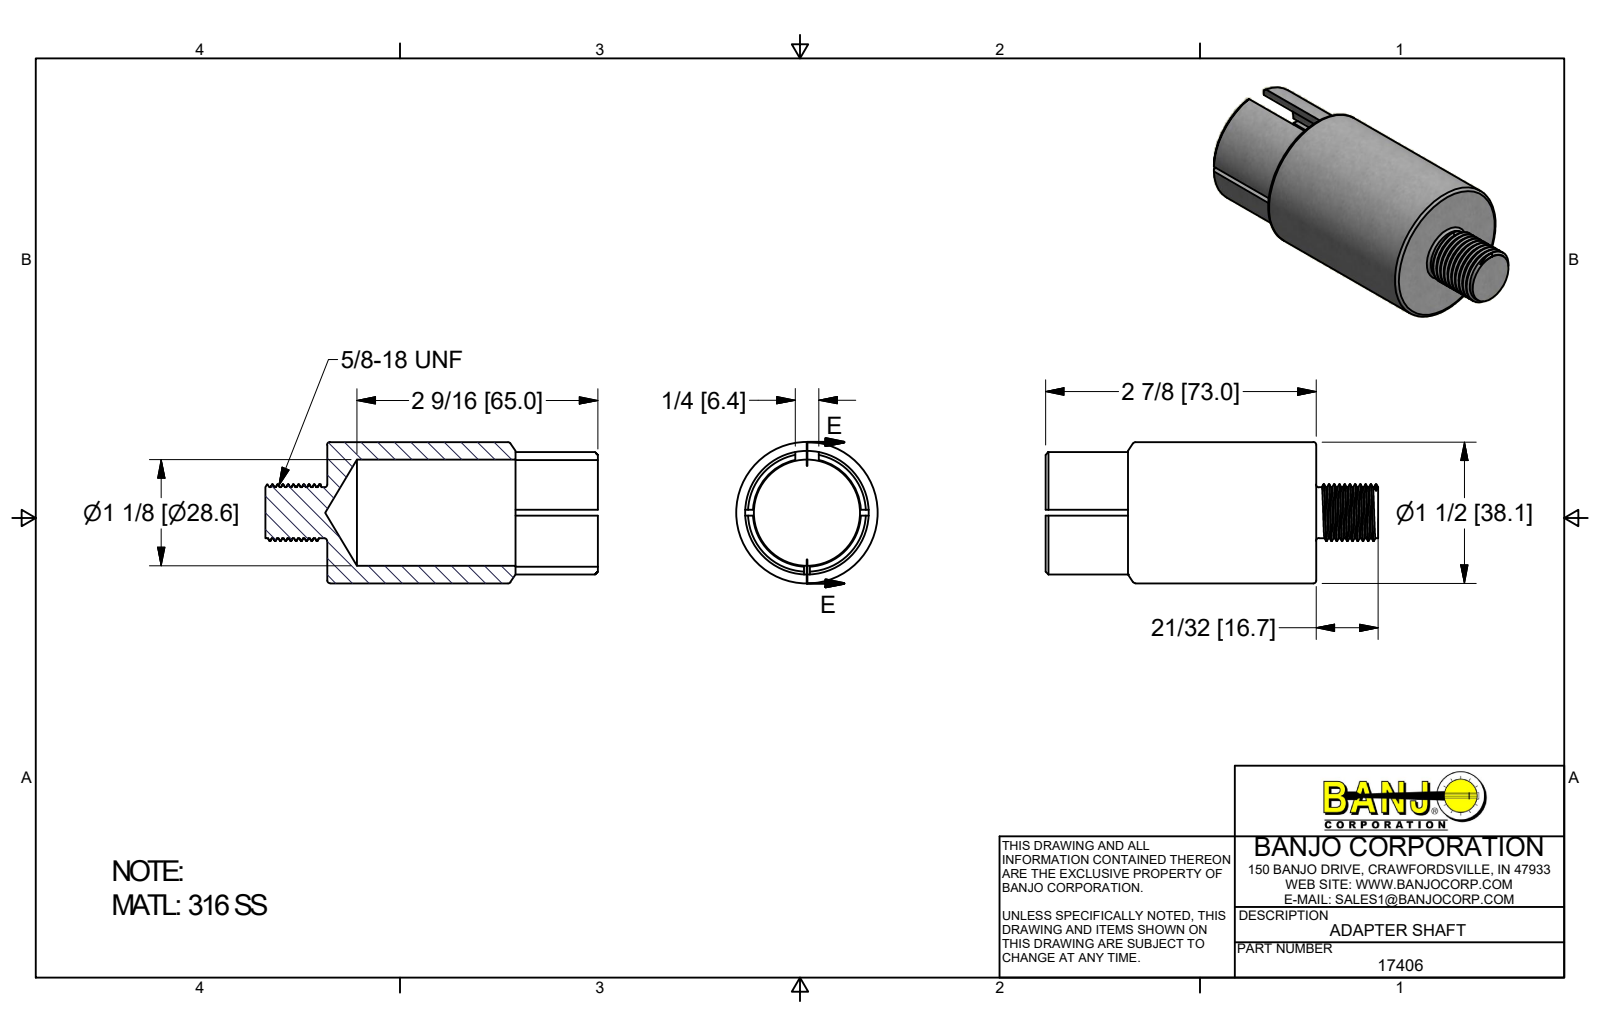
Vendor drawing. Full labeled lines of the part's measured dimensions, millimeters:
Part name (STEP PRODUCT): 17406
STEP written by: Autodesk Inventor 2017 (AUTOMOTIVE_DESIGN)
Units: millimetres
Bodies: 1 solid, 56 faces (15 planar, 26 cylindrical, 15 other)
Overall size (bounding box): 89.74 × 38.1 × 38.1
Volume: 35 121 mm³ · Surface area: 17 485 mm²
Round holes (diameter × count): ⌀28.6 ×1, ⌀29.11 ×1
Round bosses / shafts (diameter × count): ⌀38.1 ×1, ⌀33.35 ×1, ⌀15.31 ×1, ⌀13.74 ×1
Partial cylindrical surfaces — rounded edges, fillets, slot ends (radius × count): R4.22 ×2
Main face-to-face distances: 16.72, 1.58, 73.02, 89.74, 2.38, 3.96, 6.34, 22.22, 50.8, 67.52
